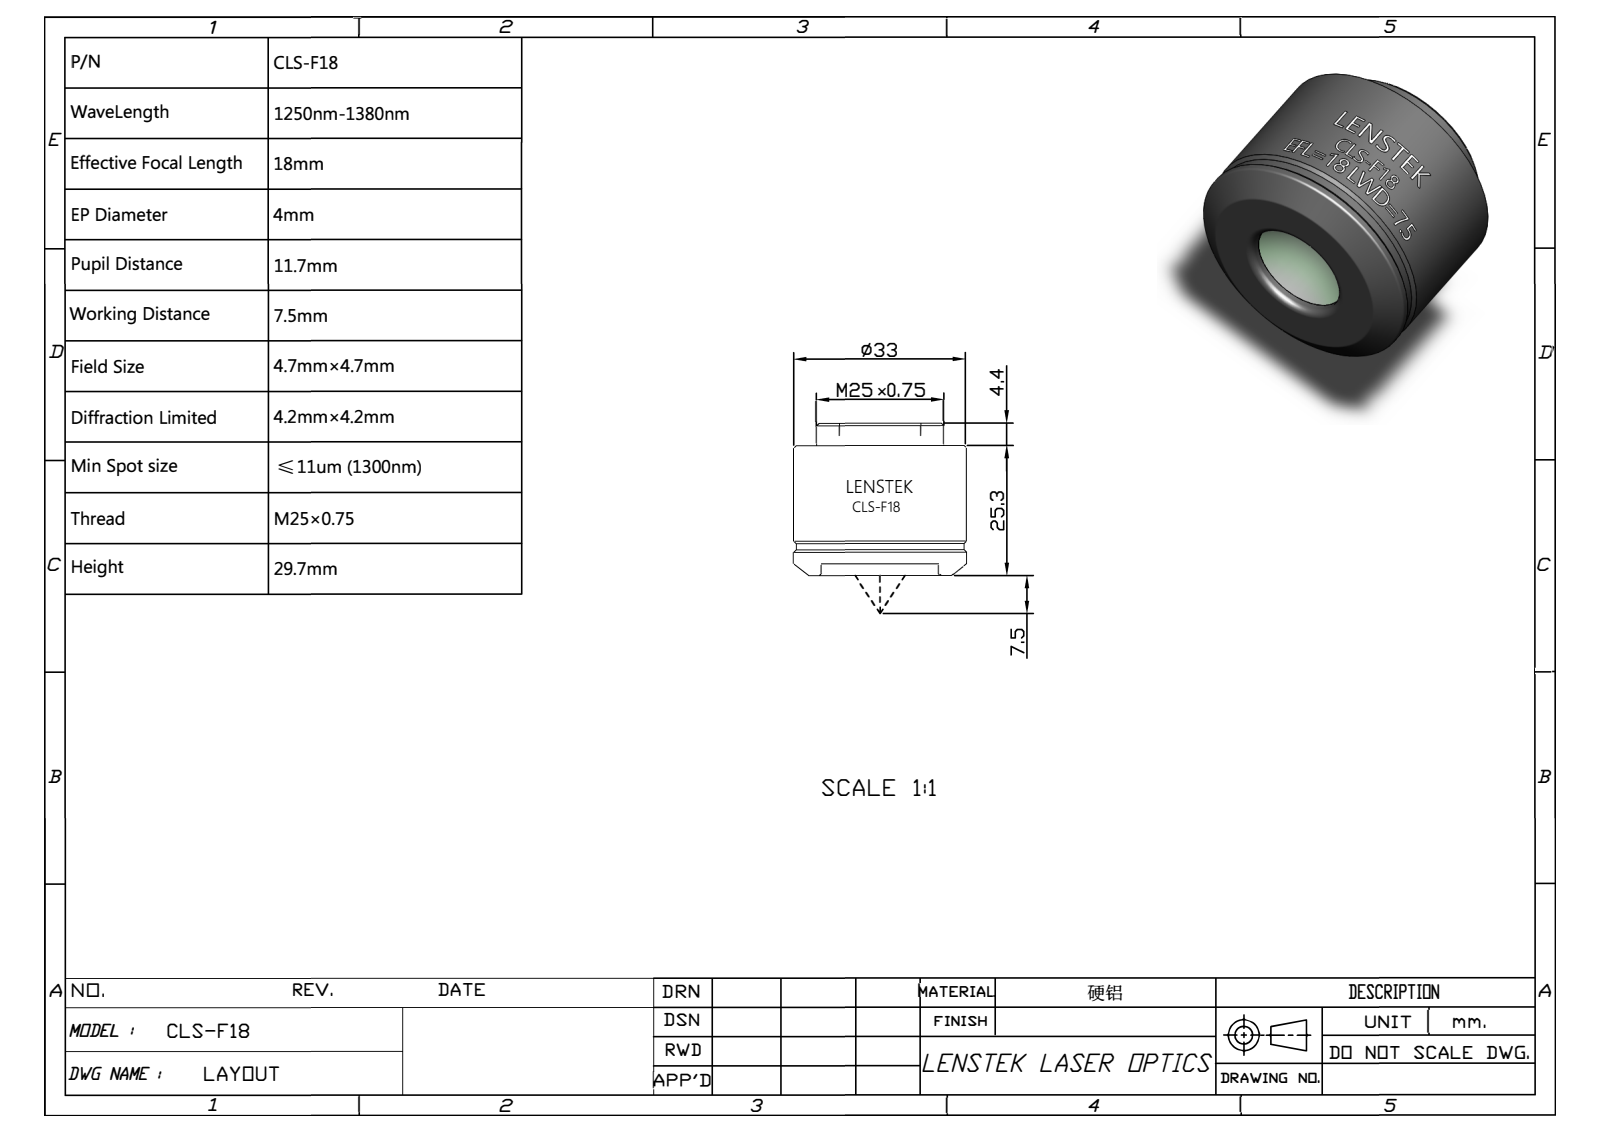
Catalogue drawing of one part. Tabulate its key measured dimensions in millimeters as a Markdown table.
| quantity | value |
| --- | --- |
| part name | CLS-F18 |
| STEP written by | SolidWorks 2018 (AUTOMOTIVE_DESIGN) |
| units | millimeters |
| bodies | 0 solids, 175 faces (77 planar, 43 cylindrical, 55 other) |
| overall size | 33 × 33 × 27.5 |
| round holes (diameter × count) | 14 × 1, 28 × 1 |
| round bosses / shafts (diameter × count) | 33 × 1, 32 × 1, 25 × 1 |
| partial cylindrical surfaces (radius × count) | 16.49 × 1 |
| main face-to-face distances | 27.5, 4.3, 23.2, 4.6, 22.9, 25.8, 21.5, 21.2, 1.7, 1 |
